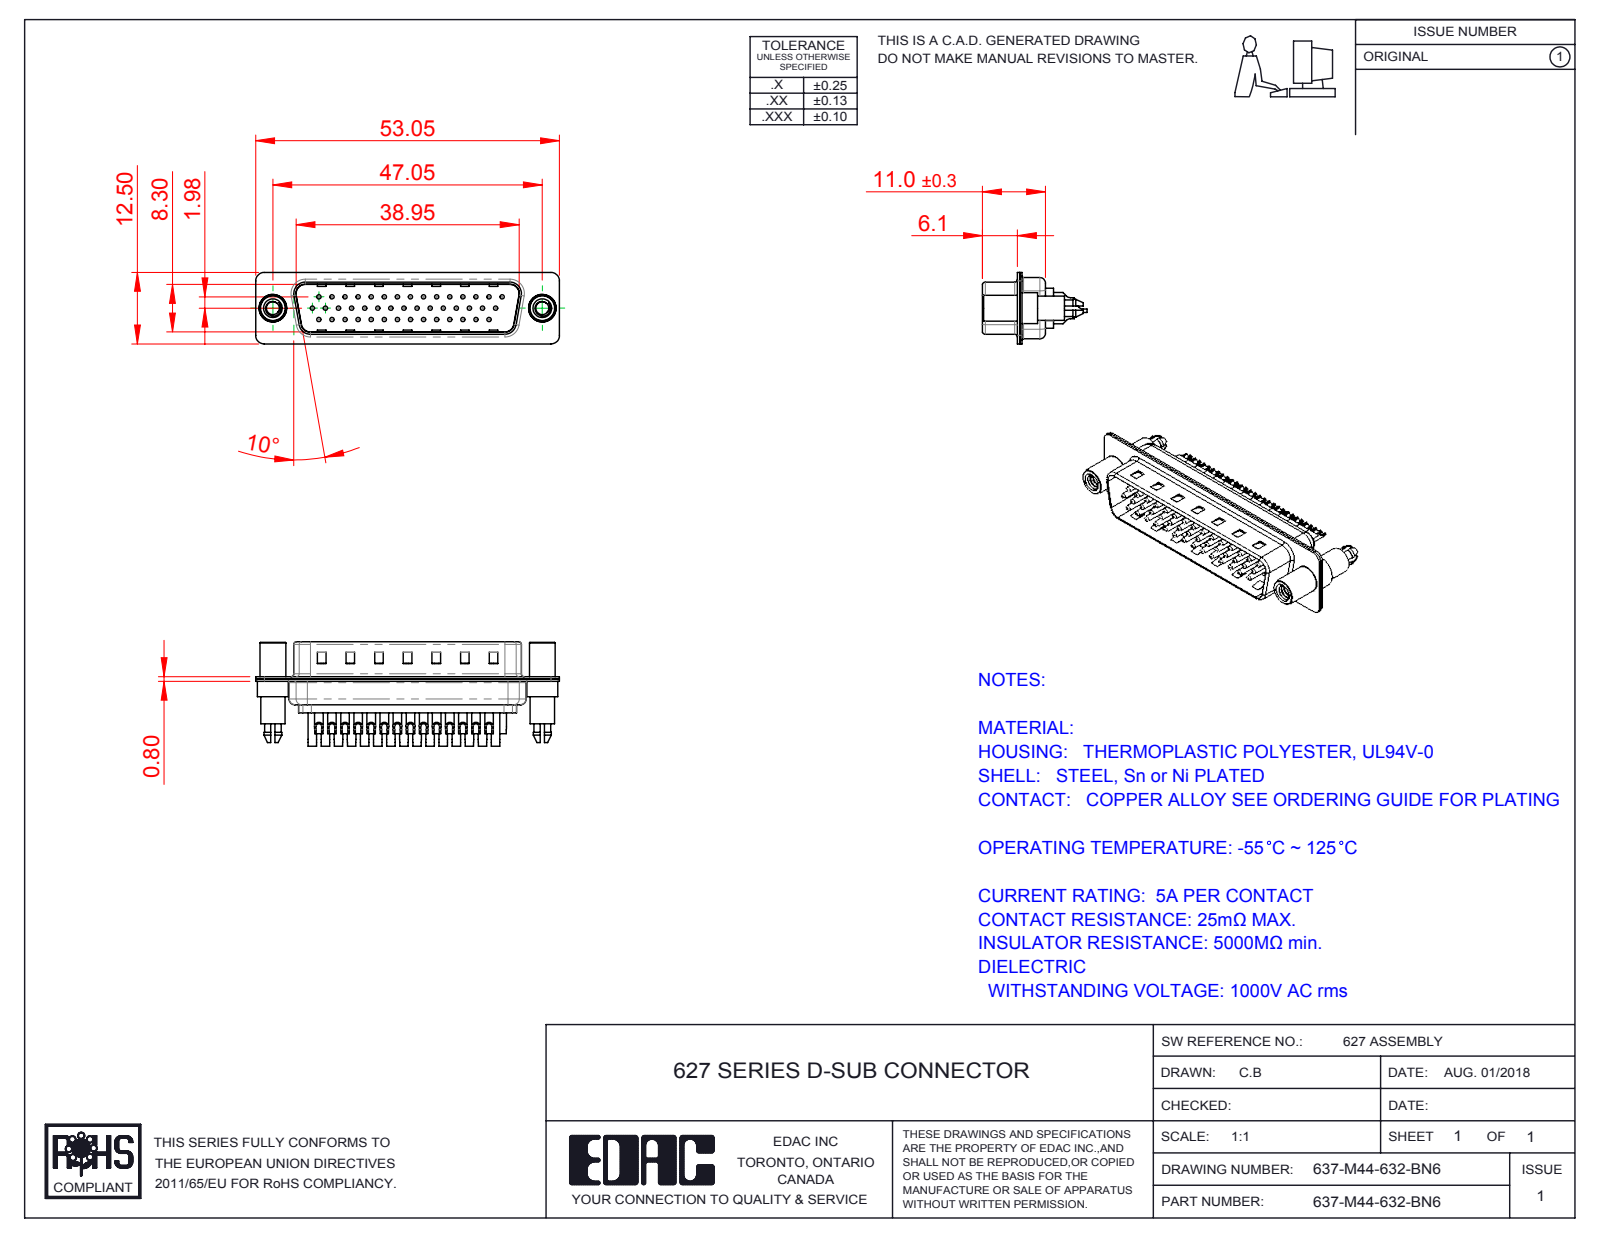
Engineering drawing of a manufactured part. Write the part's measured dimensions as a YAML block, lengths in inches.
part_name: "637M Housing_44 Contacts; 637M Contact Row 3_32; 637M Contact Row 2_32; 637M Shell Rear_44 Contacts (+4 more)"
step_written_by: "SolidWorks 2016 (CONFIG_CONTROL_DESIGN)"
units: inches
bodies: {solids: 49, faces: 2088, planar: 605, cylindrical: 877, other: 606}
overall_size: [2.089, 0.719, 0.492]
volume: 0.202
surface_area: 14.72
round_holes:
  - {diameter: 0.03, count: 44}
  - {diameter: 0.039, count: 44}
  - {diameter: 0.063, count: 44}
  - {diameter: 0.079, count: 44}
  - {diameter: 0.089, count: 2}
  - {diameter: 0.157, count: 2}
  - {diameter: 0.189, count: 2}
round_bosses_or_shafts:
  - {diameter: 0.059, count: 44}
  - {diameter: 0.079, count: 3}
  - {diameter: 0.03, count: 3}
  - {diameter: 0.213, count: 2}
  - {diameter: 0.193, count: 2}
  - {diameter: 0.177, count: 2}
  - {diameter: 0.167, count: 2}
partial_cylinders:
  - {radius: 0.059, count: 18}
  - {radius: 0.079, count: 12}
  - {radius: 0.063, count: 10}
  - {radius: 0.02, count: 8}
  - {radius: 0.039, count: 7}
  - {radius: 0.01, count: 4}
  - {radius: 0.024, count: 4}
  - {radius: 0.026, count: 4}
face_to_face_distances: [0.016, 0.031, 0.374, 0.358, 0.343, 0.39, 0.03, 0.043, 0.014, 0.075]
hole_center_spacings: [0.09, 0.156, 0.09, 0.18, 0.324, 0.27, 0.45, 0.59]
